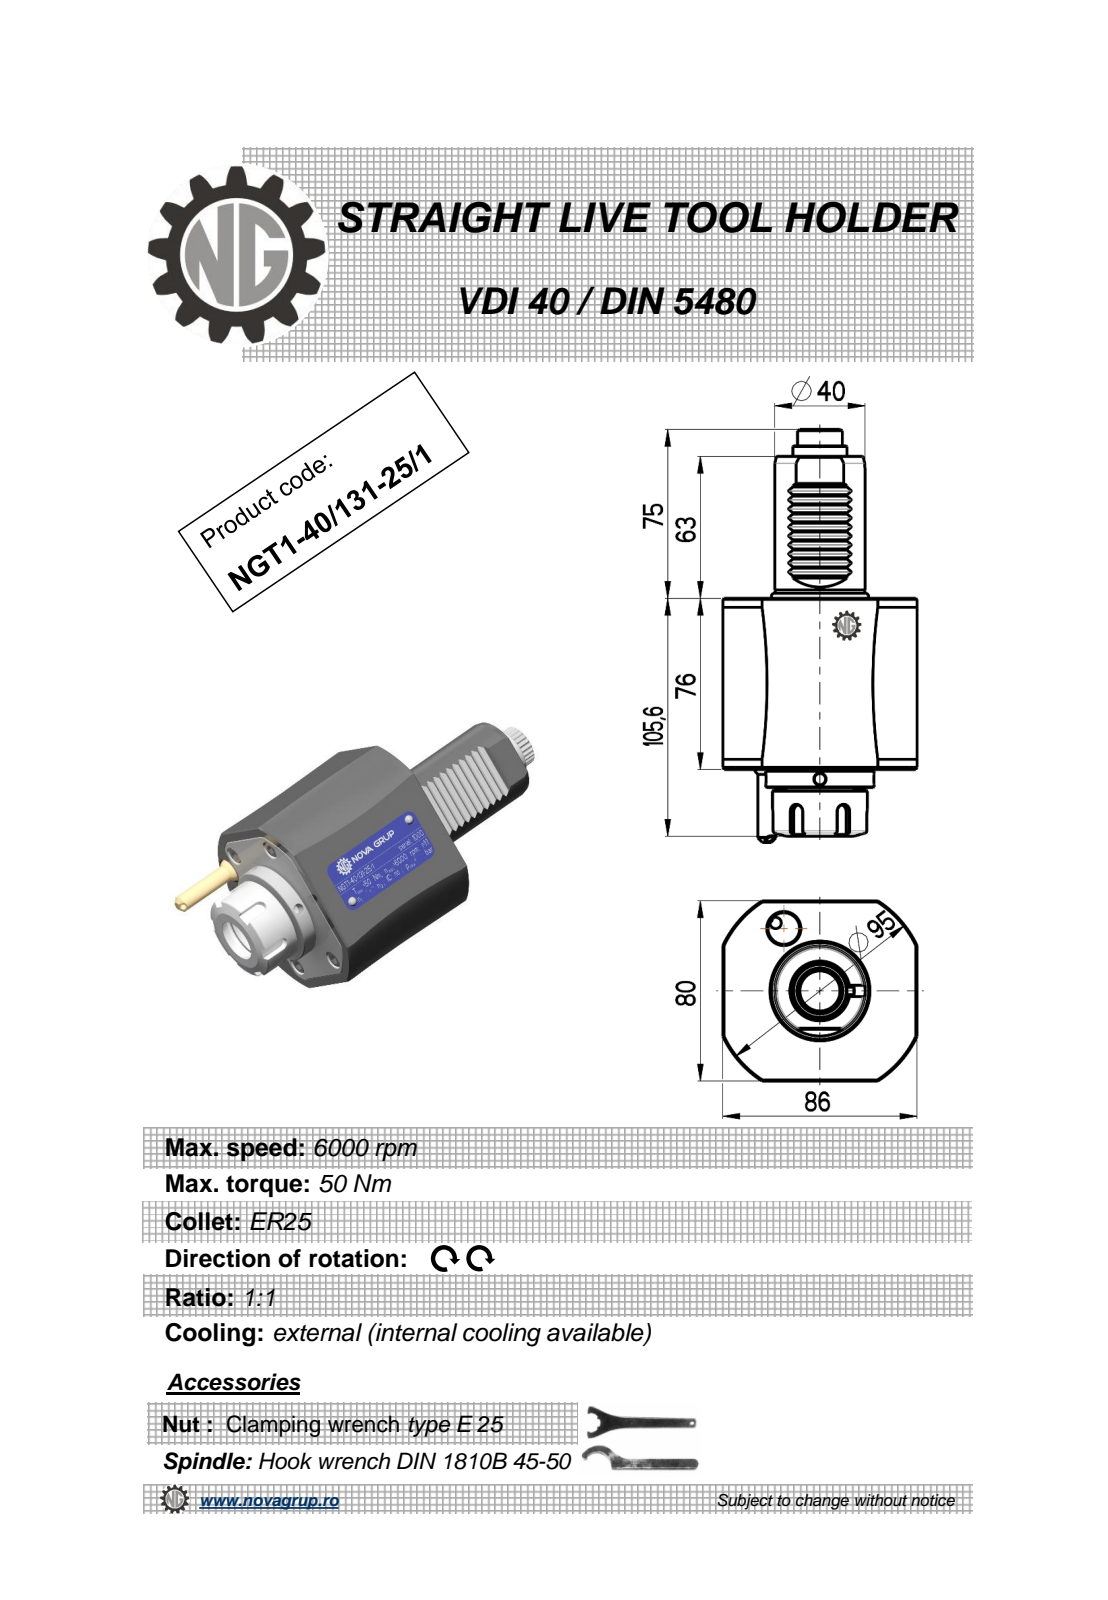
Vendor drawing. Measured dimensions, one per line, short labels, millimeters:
name: NGT1_40_131_25_1
written by: PRO/ENGINEER BY PARAMETRIC TECHNOLOGY CORPORATION, 2010280 (CONFIG_CONTROL_DESIGN)
unit: mm
bodies: 1 solid, 396 faces (106 planar, 162 cylindrical, 128 other)
size: 183.34 × 86 × 80
volume: 594 250 mm³; area: 52 119 mm²
holes: 3× ⌀5, 1× ⌀3, 1× ⌀20.3
bosses: 1× ⌀48, 1× ⌀42, 1× ⌀41.5, 1× ⌀40, 1× ⌀33, 1× ⌀24, 1× ⌀11.2, 1× ⌀8
rounds: 48× R2.08, 10× R0.3, 6× R0.22, 5× R3, 1× R9.08, 1× R9.92, 1× R15, 1× R47.5
face distances: 76, 80, 86, 84, 8, 2.83, 5.66, 63, 139, 147
hole spacings: 40
